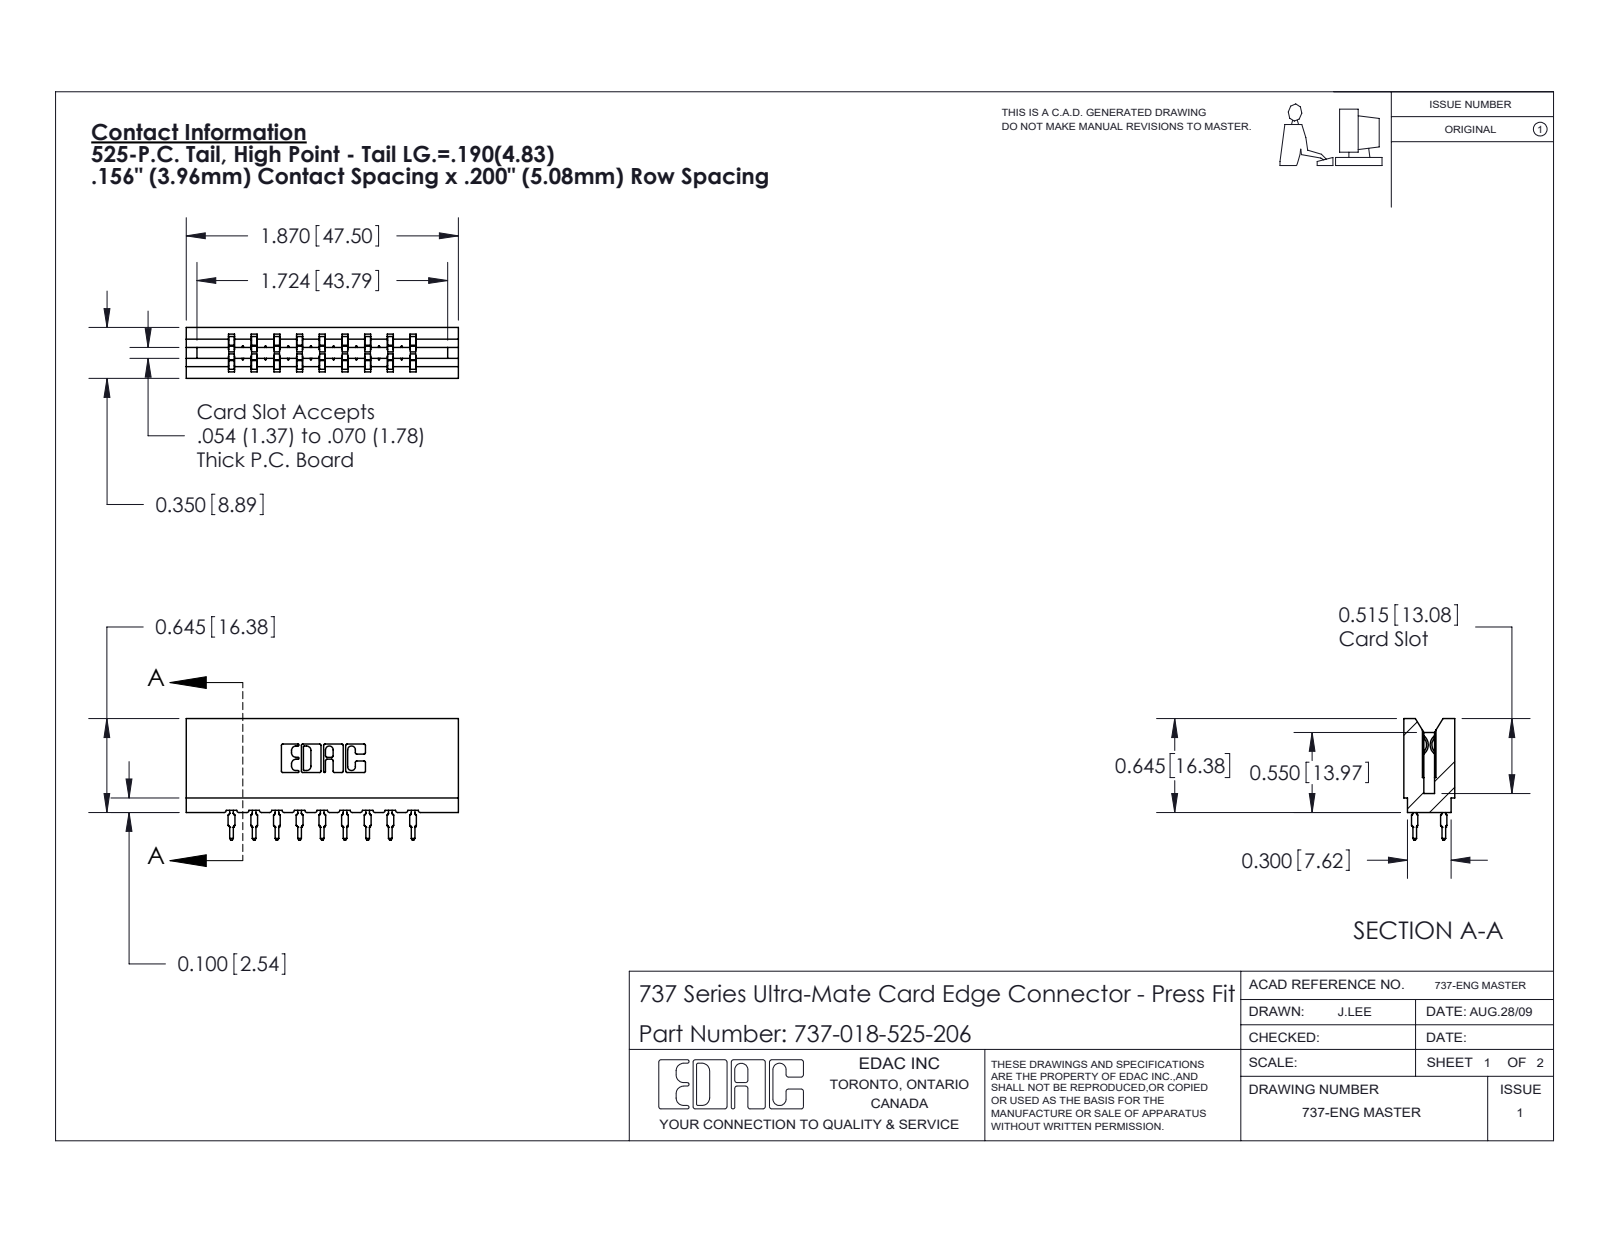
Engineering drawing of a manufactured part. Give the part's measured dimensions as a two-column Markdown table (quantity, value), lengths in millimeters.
| quantity | value |
| --- | --- |
| part name | 737 Part_Insulator Option - 06; 737-018-525-206; 745-292-001_525 |
| STEP written by | SolidWorks 2020 (CONFIG_CONTROL_DESIGN) |
| units | millimeters |
| bodies | 19 solids, 1715 faces (892 planar, 355 cylindrical, 468 other) |
| overall size | 47.5 × 21.2 × 8.9 |
| volume | 4 880 mm³ |
| surface area | 6 343 mm² |
| partial cylindrical surfaces (radius × count) | 0.5 × 36, 0.3 × 22, 0.4 × 18, 0.1 × 8, 0.3 × 8, 0.2 × 6, 0.8 × 6, 0.7 × 3 |
| main face-to-face distances | 4, 3.5, 5.4, 15.8, 8.9, 7.9, 11.9, 9, 5, 19.8 |
